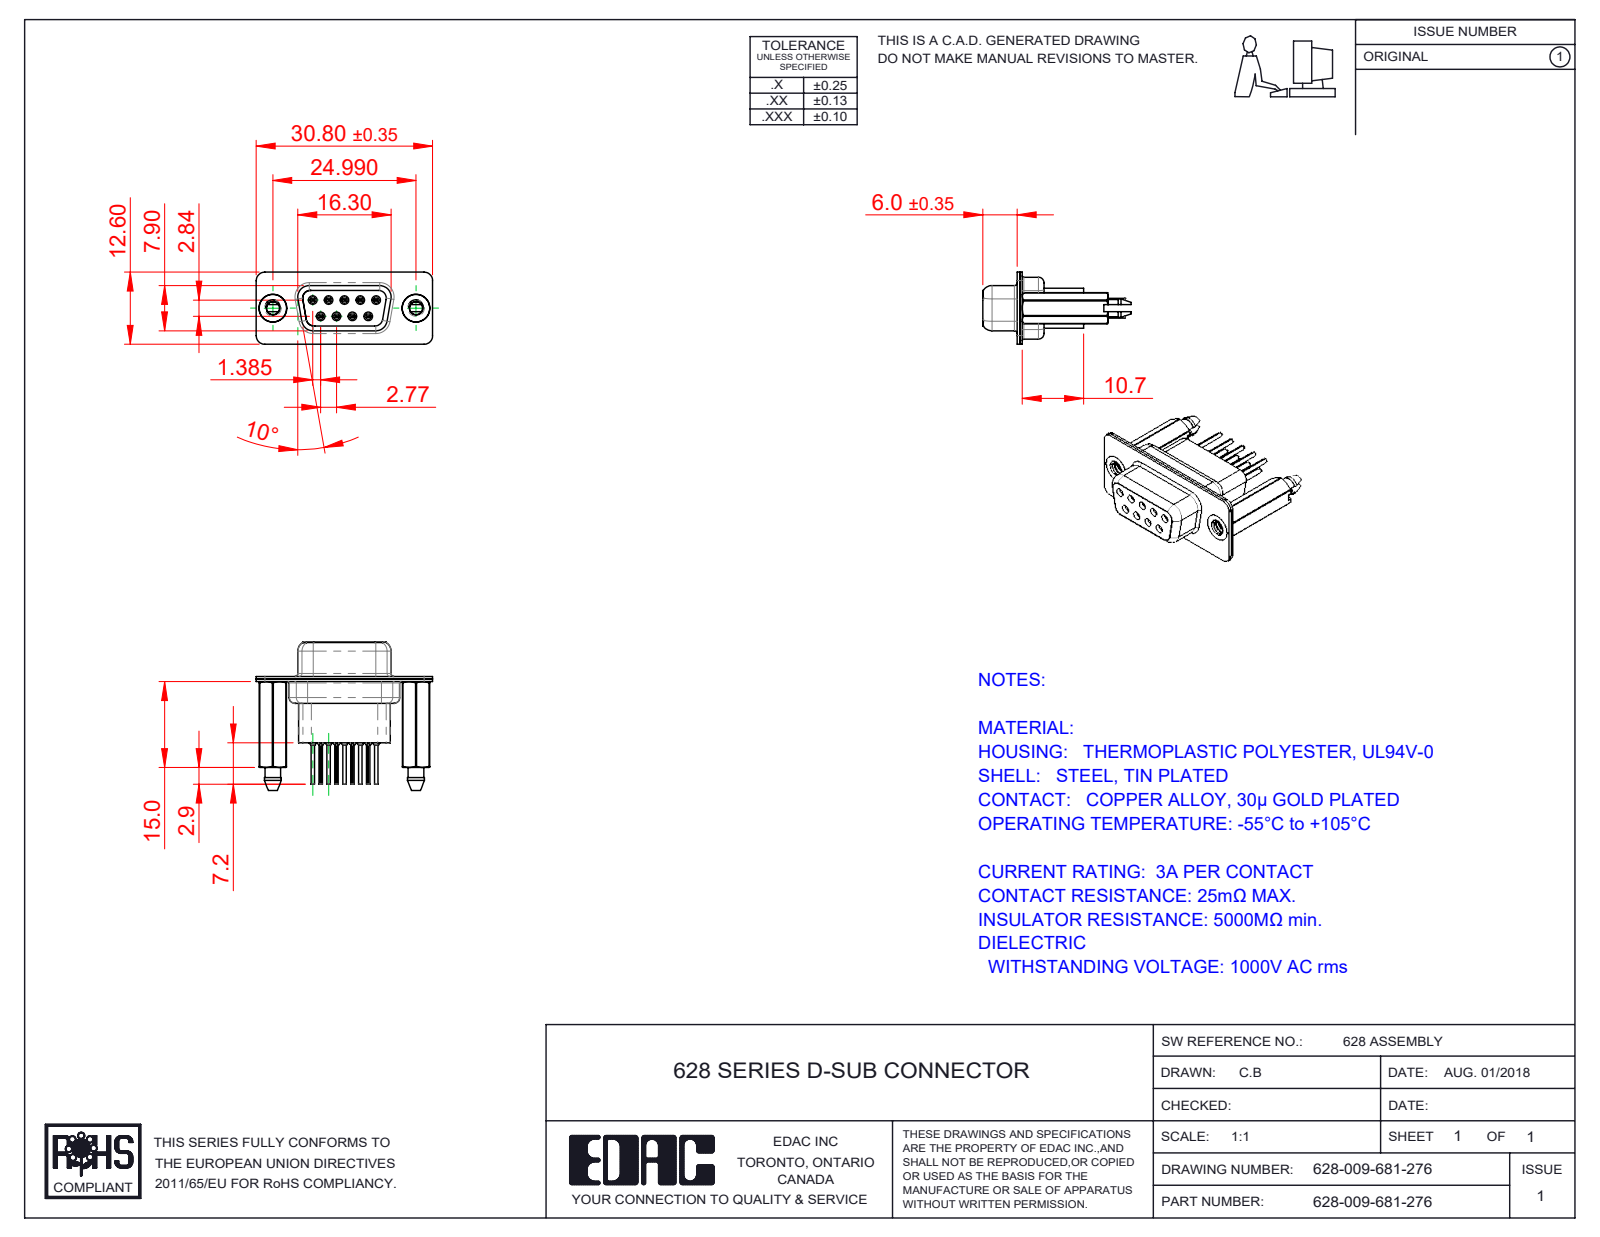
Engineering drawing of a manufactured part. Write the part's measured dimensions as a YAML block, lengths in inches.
part_name: "628 Shell Rear_09 Contacts; 628 Contact Row 1_71; 628 Contact Row 2_71; 628 Shell Front_09 Contacts (+3 more)"
step_written_by: "SolidWorks 2020 (CONFIG_CONTROL_DESIGN)"
units: inches
bodies: {solids: 14, faces: 1460, planar: 378, cylindrical: 466, other: 616}
overall_size: [1.213, 1.02, 0.496]
volume: 0.161
surface_area: 9.491
round_holes:
  - {diameter: 0.008, count: 9}
  - {diameter: 0.031, count: 9}
  - {diameter: 0.035, count: 9}
  - {diameter: 0.043, count: 9}
  - {diameter: 0.063, count: 9}
  - {diameter: 0.067, count: 5}
  - {diameter: 0.089, count: 2}
  - {diameter: 0.157, count: 2}
  - {diameter: 0.159, count: 2}
  - {diameter: 0.191, count: 2}
round_bosses_or_shafts:
  - {diameter: 0.079, count: 9}
  - {diameter: 0.059, count: 9}
  - {diameter: 0.047, count: 9}
  - {diameter: 0.024, count: 9}
  - {diameter: 0.195, count: 2}
  - {diameter: 0.189, count: 2}
partial_cylinders:
  - {radius: 0.059, count: 19}
  - {radius: 0.004, count: 18}
  - {radius: 0.079, count: 12}
  - {radius: 0.011, count: 9}
  - {radius: 0.053, count: 6}
  - {radius: 0.063, count: 6}
  - {radius: 0.01, count: 4}
  - {radius: 0.02, count: 4}
face_to_face_distances: [0.018, 0.016, 0.035, 0.335, 0.26, 0.187, 0.075, 0.055, 0.276, 0.421]
hole_center_spacings: [0.124, 0.109, 0.218, 0.198, 0.198, 0.327, 0.294, 0.295]
